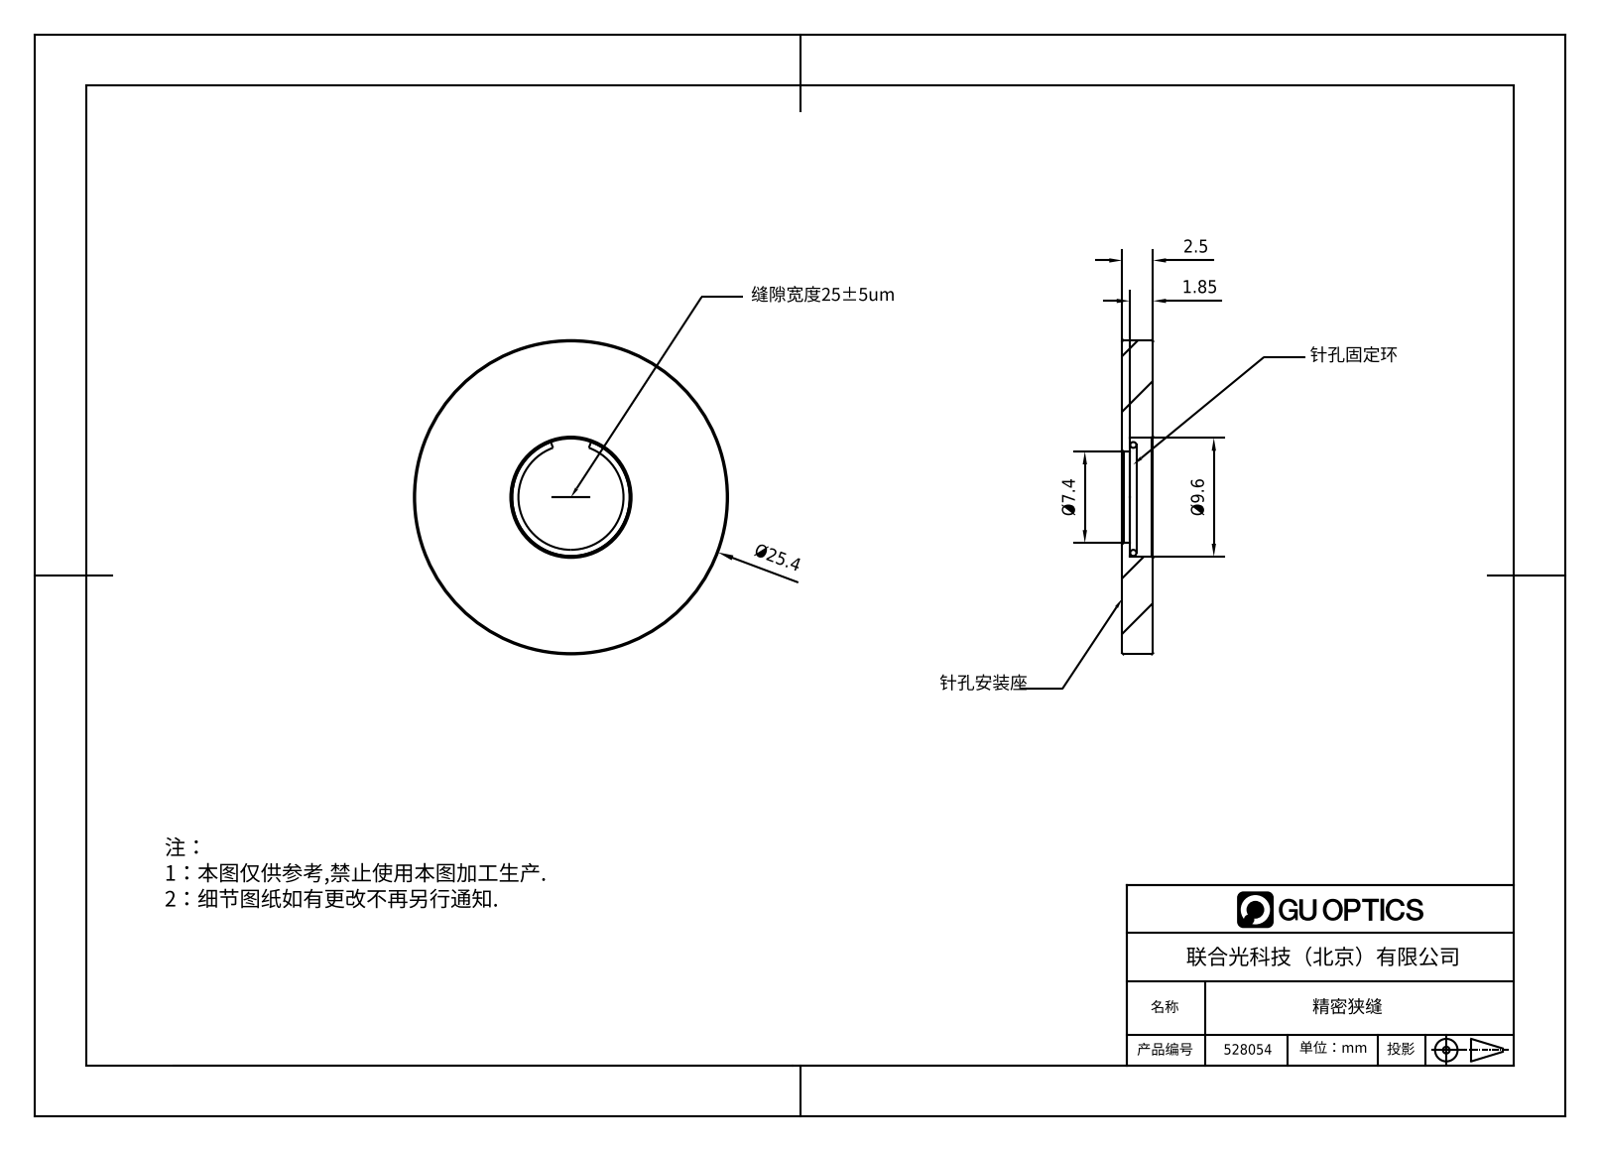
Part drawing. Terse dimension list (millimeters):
name: 528054
written by: SolidWorks 2020 (CONFIG_CONTROL_DESIGN)
unit: mm
bodies: 2 solids, 33 faces (11 planar, 8 cylindrical, 14 other)
size: 25.4 × 25.4 × 2.5
volume: 1 111 mm³; area: 1 313 mm²
holes: 1× ⌀7.4, 1× ⌀9.6
bosses: 1× ⌀25.4, 1× ⌀9.5
face distances: 2.5, 0.65, 1.85, 0.6, 1.9, 3
